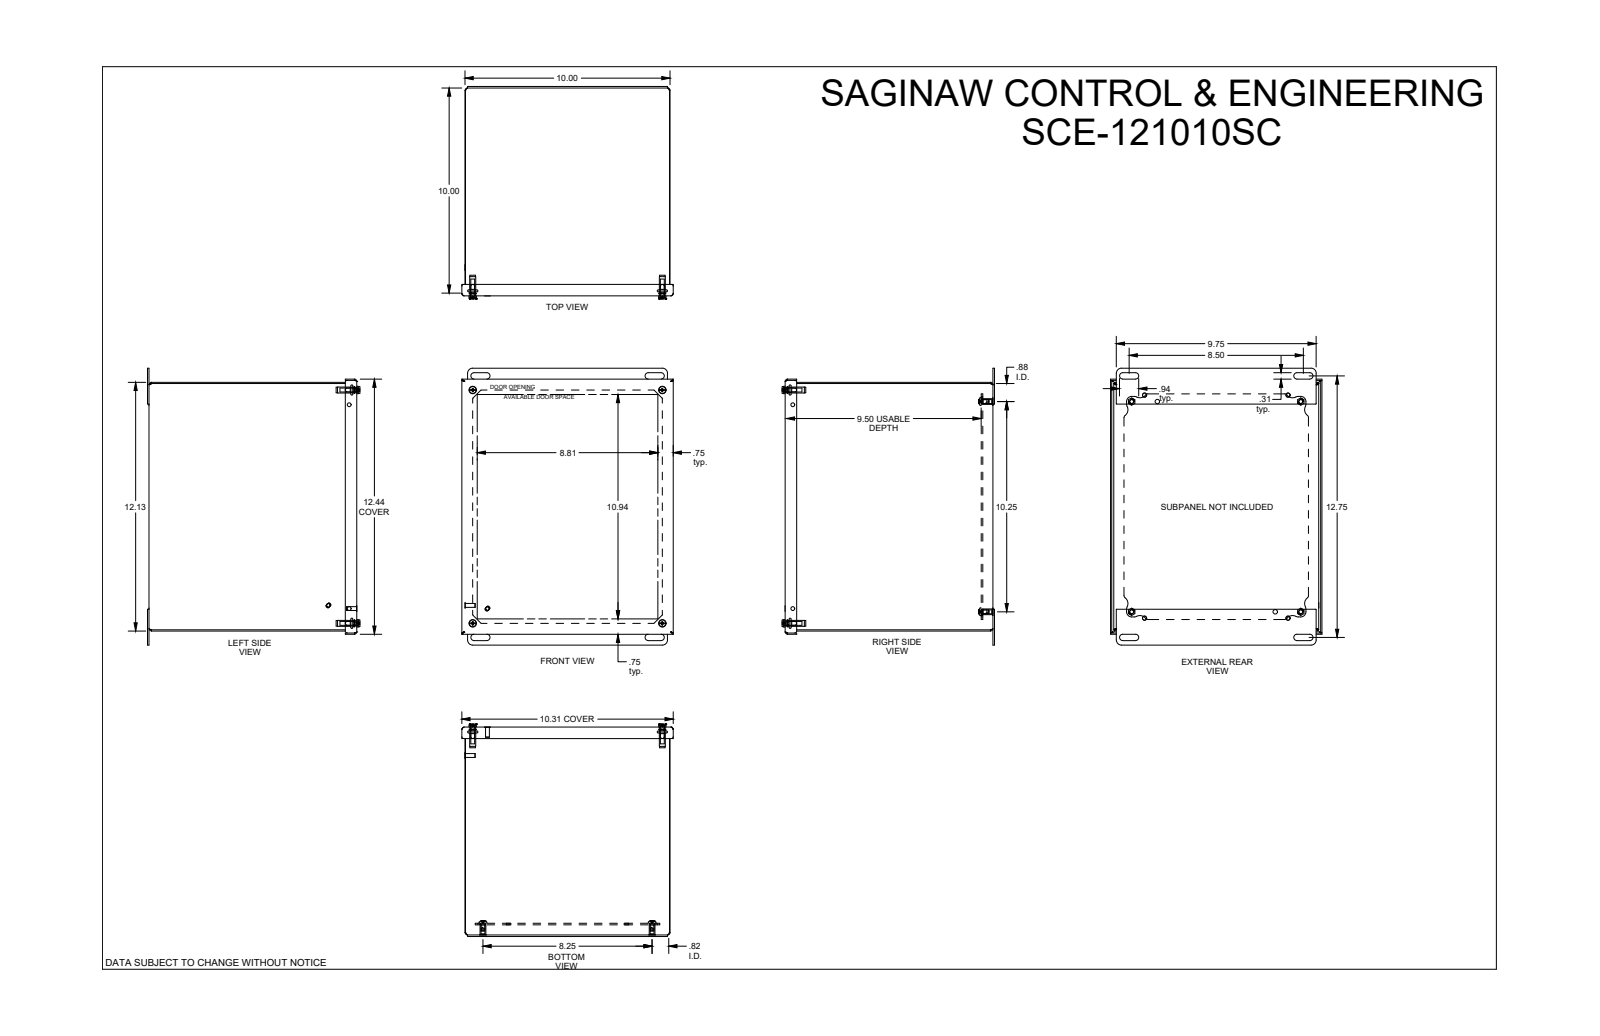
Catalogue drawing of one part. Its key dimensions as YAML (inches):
part_name: "SCE-121010SC"
step_written_by: "SolidWorks 2019 (AUTOMOTIVE_DESIGN)"
units: inches
bodies: {solids: 28, faces: 809, planar: 328, cylindrical: 211, other: 270}
overall_size: [13.5, 10.361, 10.313]
volume: 54.46
surface_area: 1760
round_holes:
  - {diameter: 0.19, count: 8}
  - {diameter: 0.25, count: 8}
  - {diameter: 0.203, count: 4}
  - {diameter: 0.22, count: 4}
  - {diameter: 0.266, count: 4}
  - {diameter: 0.281, count: 4}
  - {diameter: 0.317, count: 4}
  - {diameter: 0.187, count: 2}
  - {diameter: 0.218, count: 2}
  - {diameter: 0.193, count: 1}
round_bosses_or_shafts:
  - {diameter: 0.188, count: 10}
  - {diameter: 0.437, count: 4}
  - {diameter: 0.373, count: 4}
  - {diameter: 0.362, count: 4}
  - {diameter: 0.34, count: 4}
  - {diameter: 0.334, count: 4}
  - {diameter: 0.292, count: 4}
  - {diameter: 0.28, count: 4}
partial_cylinders:
  - {radius: 0.125, count: 16}
  - {radius: 0.25, count: 16}
  - {radius: 0.06, count: 12}
  - {radius: 0.005, count: 8}
  - {radius: 0.05, count: 8}
  - {radius: 0.063, count: 8}
  - {radius: 0.156, count: 8}
  - {radius: 0.255, count: 8}
face_to_face_distances: [0.06, 9.94, 10.075, 12.065, 9.88, 10, 10.135, 10.015, 9.505, 0.075]
hole_center_spacings: [10.824, 0.753, 13.909, 13.776, 8.768, 0.699, 1.152, 8.129]
